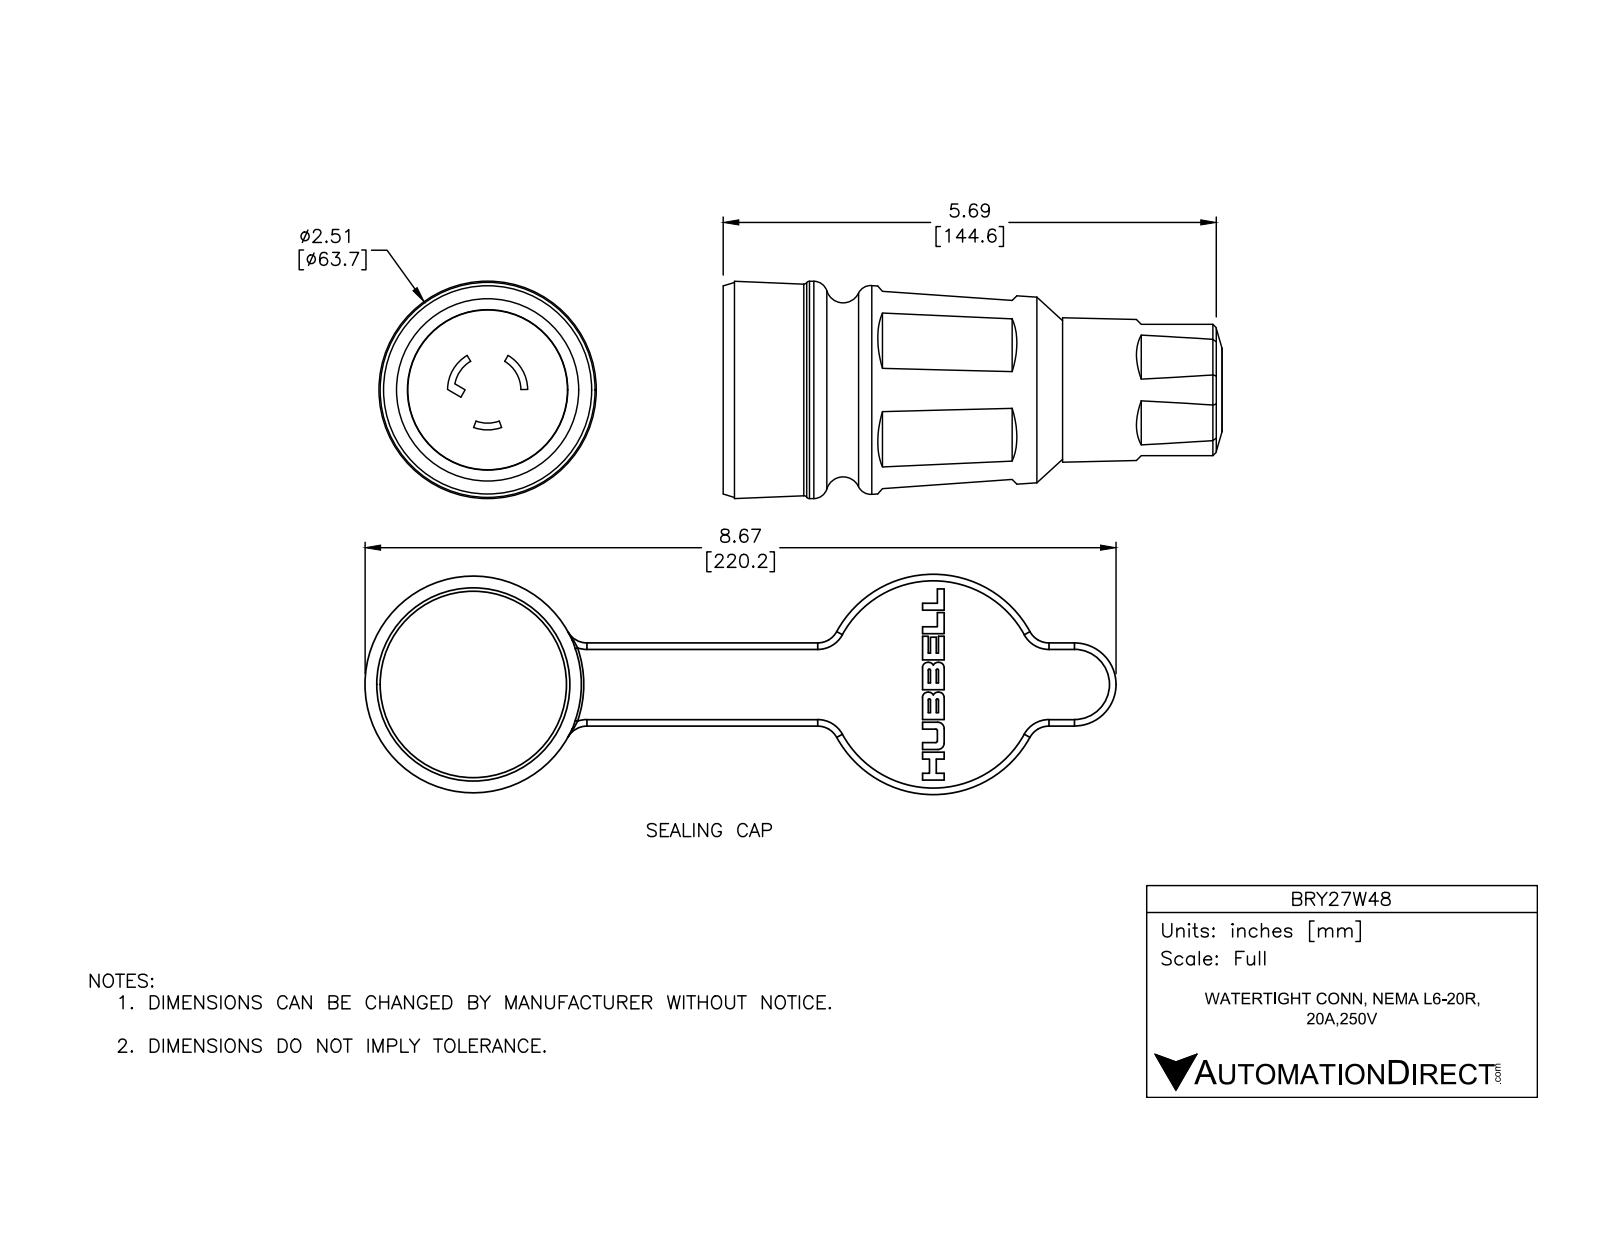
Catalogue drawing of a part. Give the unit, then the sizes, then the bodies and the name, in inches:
Units: inches
Overall size (bounding box): 8.608 × 5.759 × 2.52
Round holes (diameter × count): ⌀0.866 ×1, ⌀1.417 ×1, ⌀1.772 ×1, ⌀1.85 ×1, ⌀2.087 ×1, ⌀2.102 ×1
Round bosses / shafts (diameter × count): ⌀2.52 ×1, ⌀2.508 ×1, ⌀2.425 ×1, ⌀2.205 ×1, ⌀2.037 ×1, ⌀1.843 ×1, ⌀1.24 ×1
Partial cylindrical surfaces — rounded edges, fillets, slot ends (radius × count): R0.069 ×4, R0.236 ×4, R0.157 ×2, R0.384 ×1, R0.463 ×1, R0.482 ×1
Main face-to-face distances: 0.146, 0.502, 0.648, 1.354, 0.852, 0.706, 0.778, 0.276, 0.13, 0.576
Hole centre spacings: 5.228
Volume: 18.31 in³ · Surface area: 123.8 in²
Bodies: 5 solids, 182 faces (69 planar, 51 cylindrical, 62 other)
Part name (STEP PRODUCT): BRY27W48; BRY27W-CAP; BRY27W48-CONNECTOR
STEP written by: SolidWorks 2016 (AUTOMOTIVE_DESIGN)
